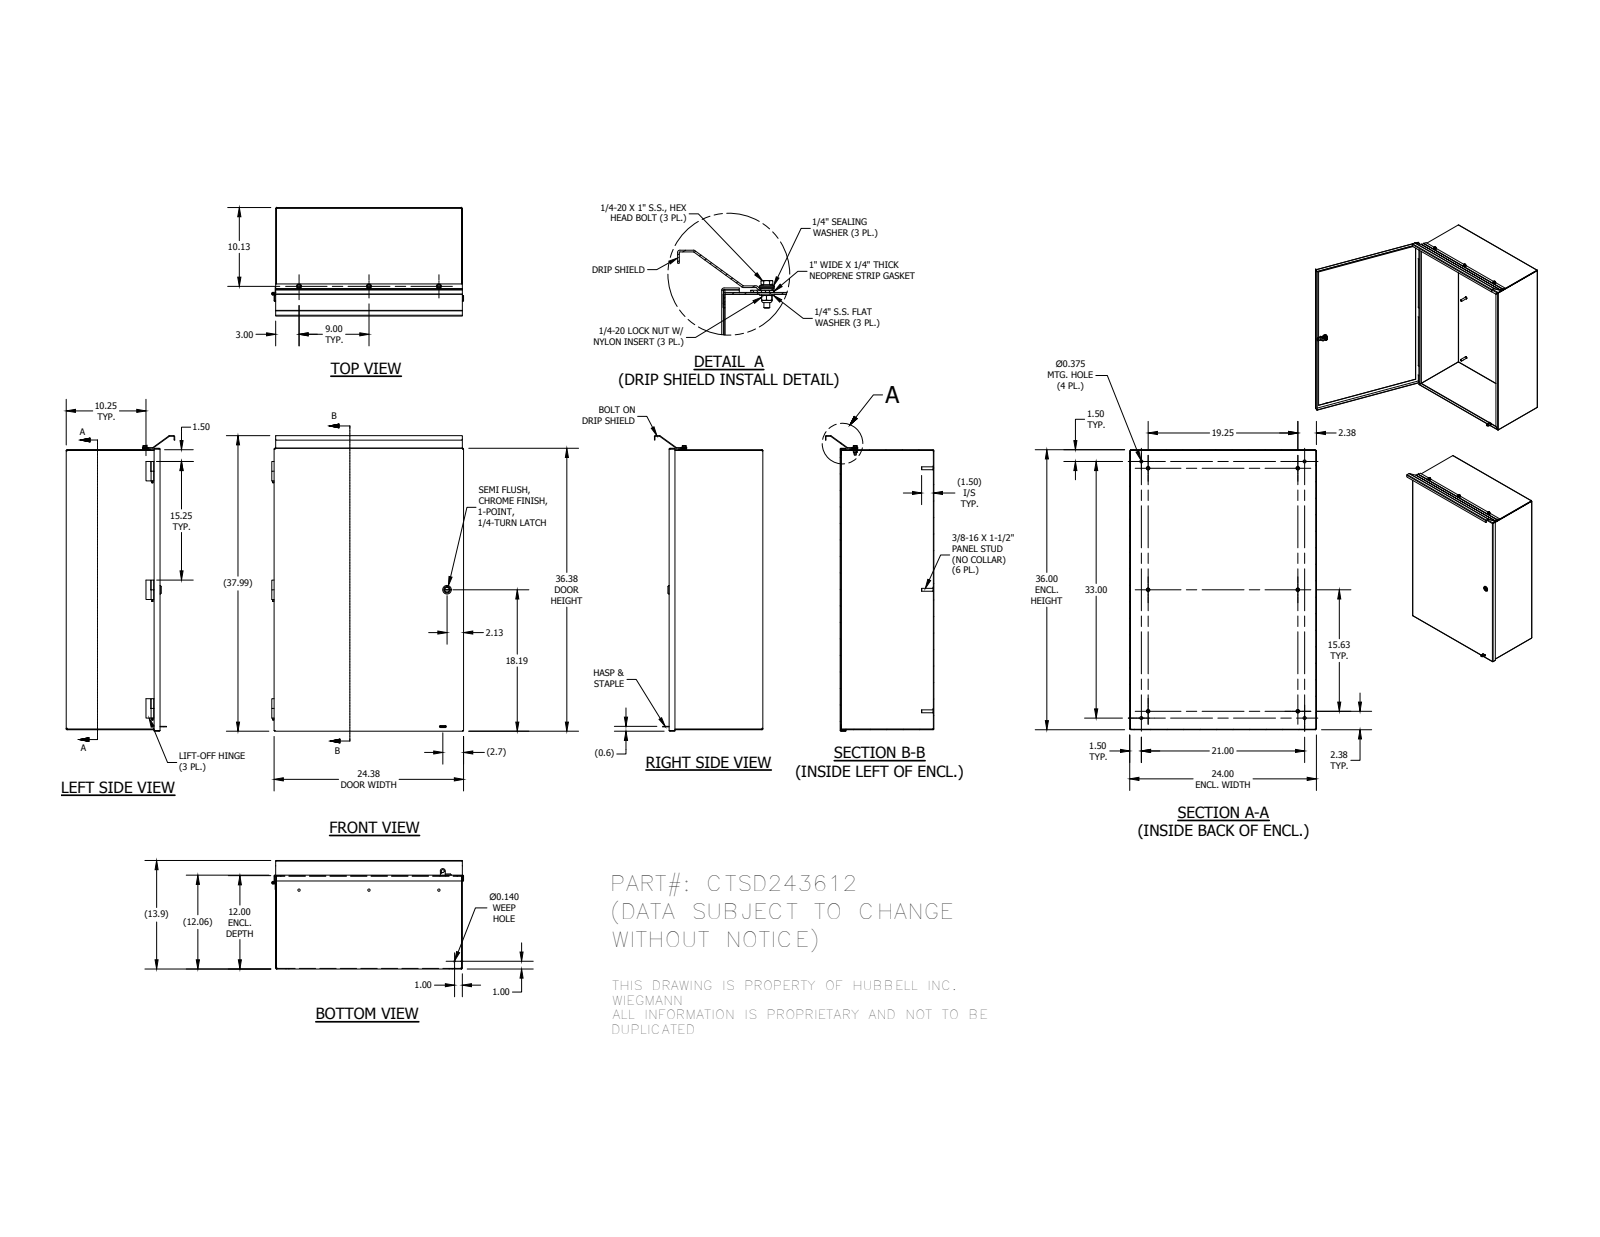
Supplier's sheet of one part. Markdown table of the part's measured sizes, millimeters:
| quantity | value |
| --- | --- |
| part name | CTSD243612BKP; CTSD2436DR; 31815; HC2527 (+8 more) |
| STEP written by | Autodesk Inventor 2014 (AUTOMOTIVE_DESIGN) |
| units | millimeters |
| bodies | 41 solids, 913 faces (488 planar, 272 cylindrical, 153 other) |
| overall size | 965.07 × 626.48 × 354.32 |
| volume | 4 337 000 mm³ |
| surface area | 4 645 000 mm² |
| round holes (diameter × count) | 9.52 × 5, 4.98 × 3, 5.97 × 3, 6.99 × 3, 7.14 × 3, 7.37 × 3, 3.17 × 1, 3.56 × 1, 5 × 1, 5.36 × 1, 5.56 × 1, 8 × 1 |
| round bosses / shafts (diameter × count) | 11.73 × 6, 9.52 × 6, 16.51 × 3, 15.88 × 3, 15.24 × 3, 11.13 × 3, 11.05 × 3, 6.6 × 3 |
| partial cylindrical surfaces (radius × count) | 0.3 × 30, 0.79 × 20, 2.67 × 18, 0.5 × 10, 1.78 × 8, 3.17 × 4, 4 × 4, 0.4 × 3 |
| main face-to-face distances | 1.88, 304.4, 302.52, 306.28, 607.72, 912.52, 609.6, 605.84, 914.4, 910.64 |
| hole center spacings | 228.6, 419.26, 533.4, 669.19, 838.2, 993.53, 7.32, 57.12 |
